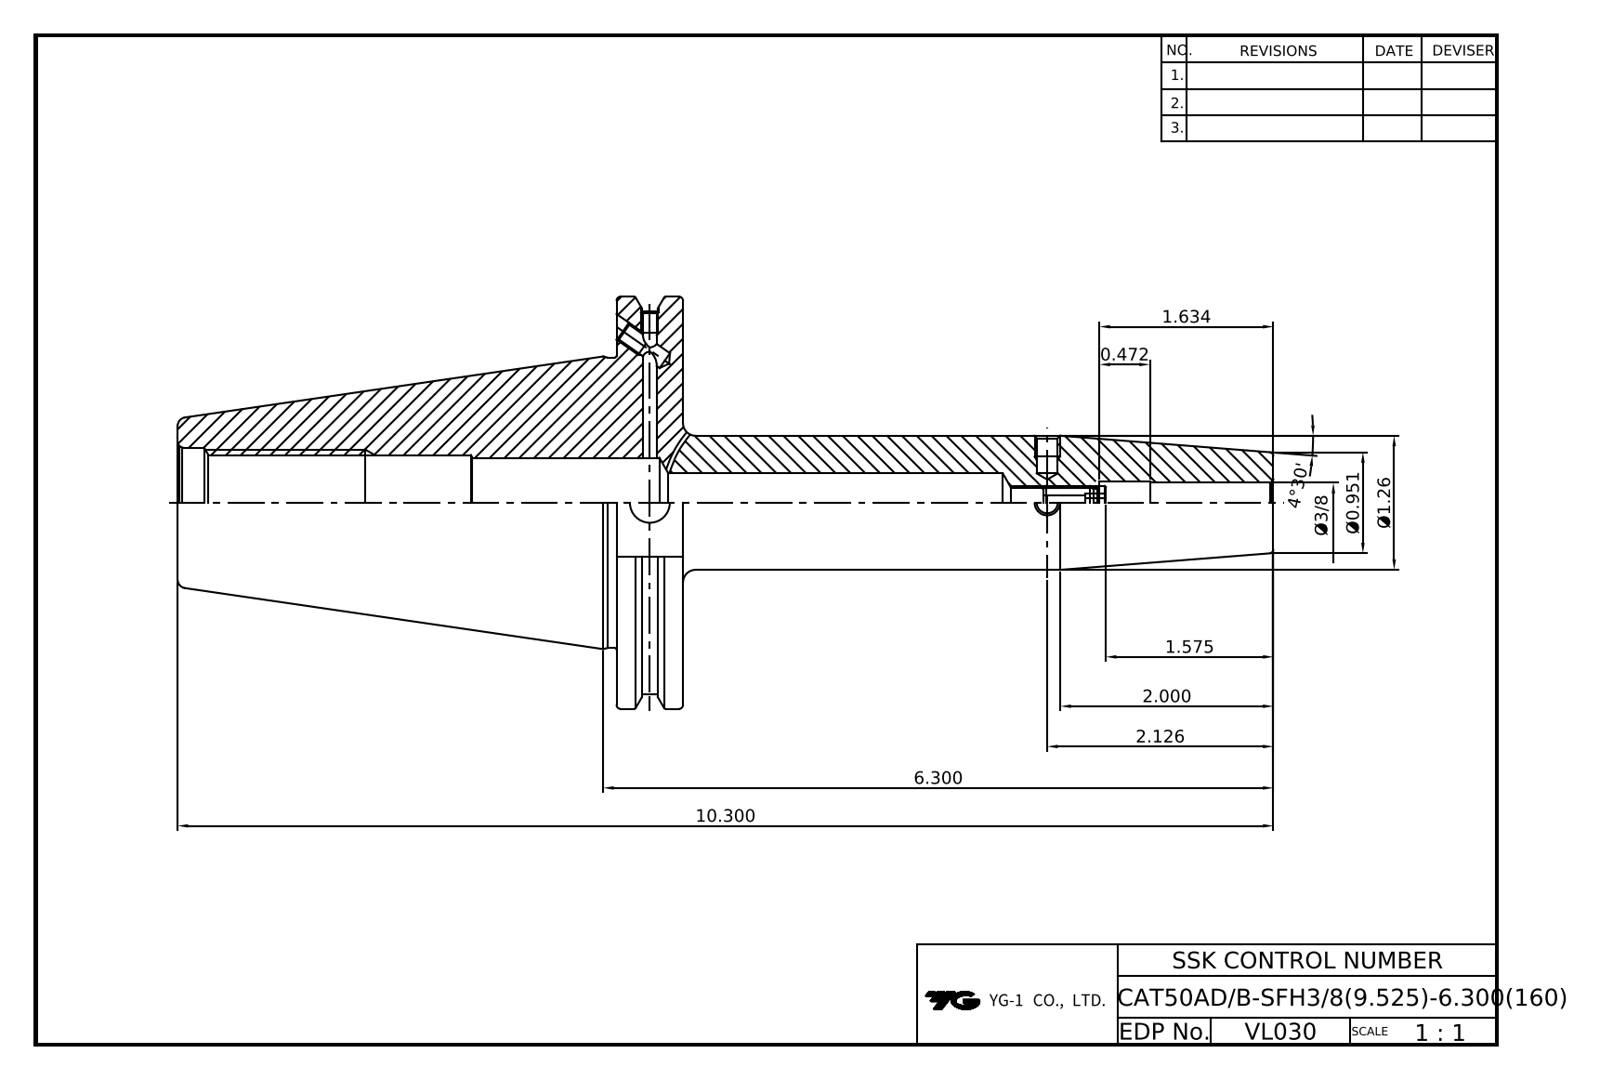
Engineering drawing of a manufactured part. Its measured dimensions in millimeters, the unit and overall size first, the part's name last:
Units: millimetres
Overall size (bounding box): 261.6 × 98.42 × 94.69
Round holes (diameter × count): ⌀3.24 ×2, ⌀4.13 ×2, ⌀4.2 ×2, ⌀5 ×2, ⌀9.53 ×2, ⌀6.92 ×1, ⌀10.73 ×1, ⌀21.97 ×1, ⌀26.2 ×1
Round bosses / shafts (diameter × count): ⌀98.42 ×1, ⌀91.29 ×1, ⌀69.25 ×1, ⌀32 ×1
Main face-to-face distances: 15.88, 104.77, 120.65, 73.03, 25.9, 261.6, 156.83, 140.95, 110.82, 6.05
Volume: 416 711 mm³ · Surface area: 61 502 mm²
Bodies: 1 solid, 84 faces (37 planar, 26 cylindrical, 21 other)
Part name (STEP PRODUCT): LO-CAT50ADB-SFH9.525-160
STEP written by: Autodesk Inventor 2025 (AUTOMOTIVE_DESIGN)
